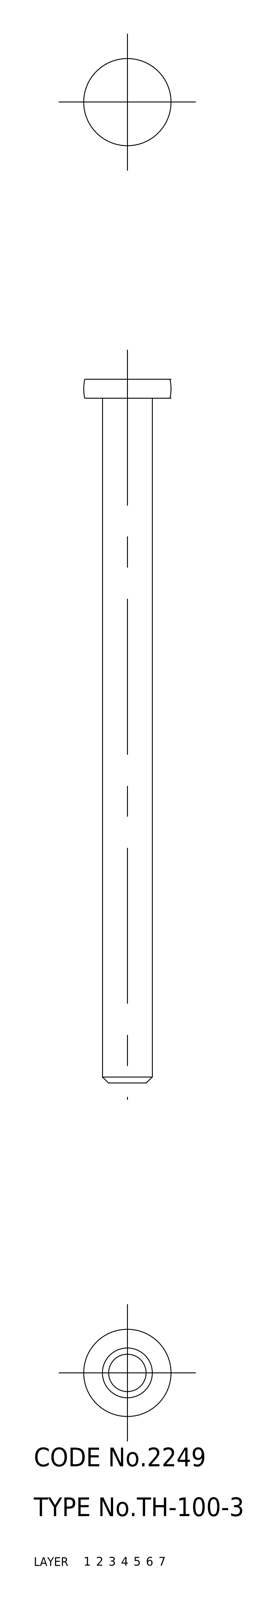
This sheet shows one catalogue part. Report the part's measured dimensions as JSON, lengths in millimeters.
{"part_name": "shaft", "step_written_by": "CADfix (AUTOMOTIVE_DESIGN)", "units": "millimeters", "bodies": {"solids": 1, "faces": 8, "planar": 0, "cylindrical": 0, "other": 8}, "overall_size": [113, 14, 14], "volume_mm3": 5984, "surface_area_mm2": 3176}
